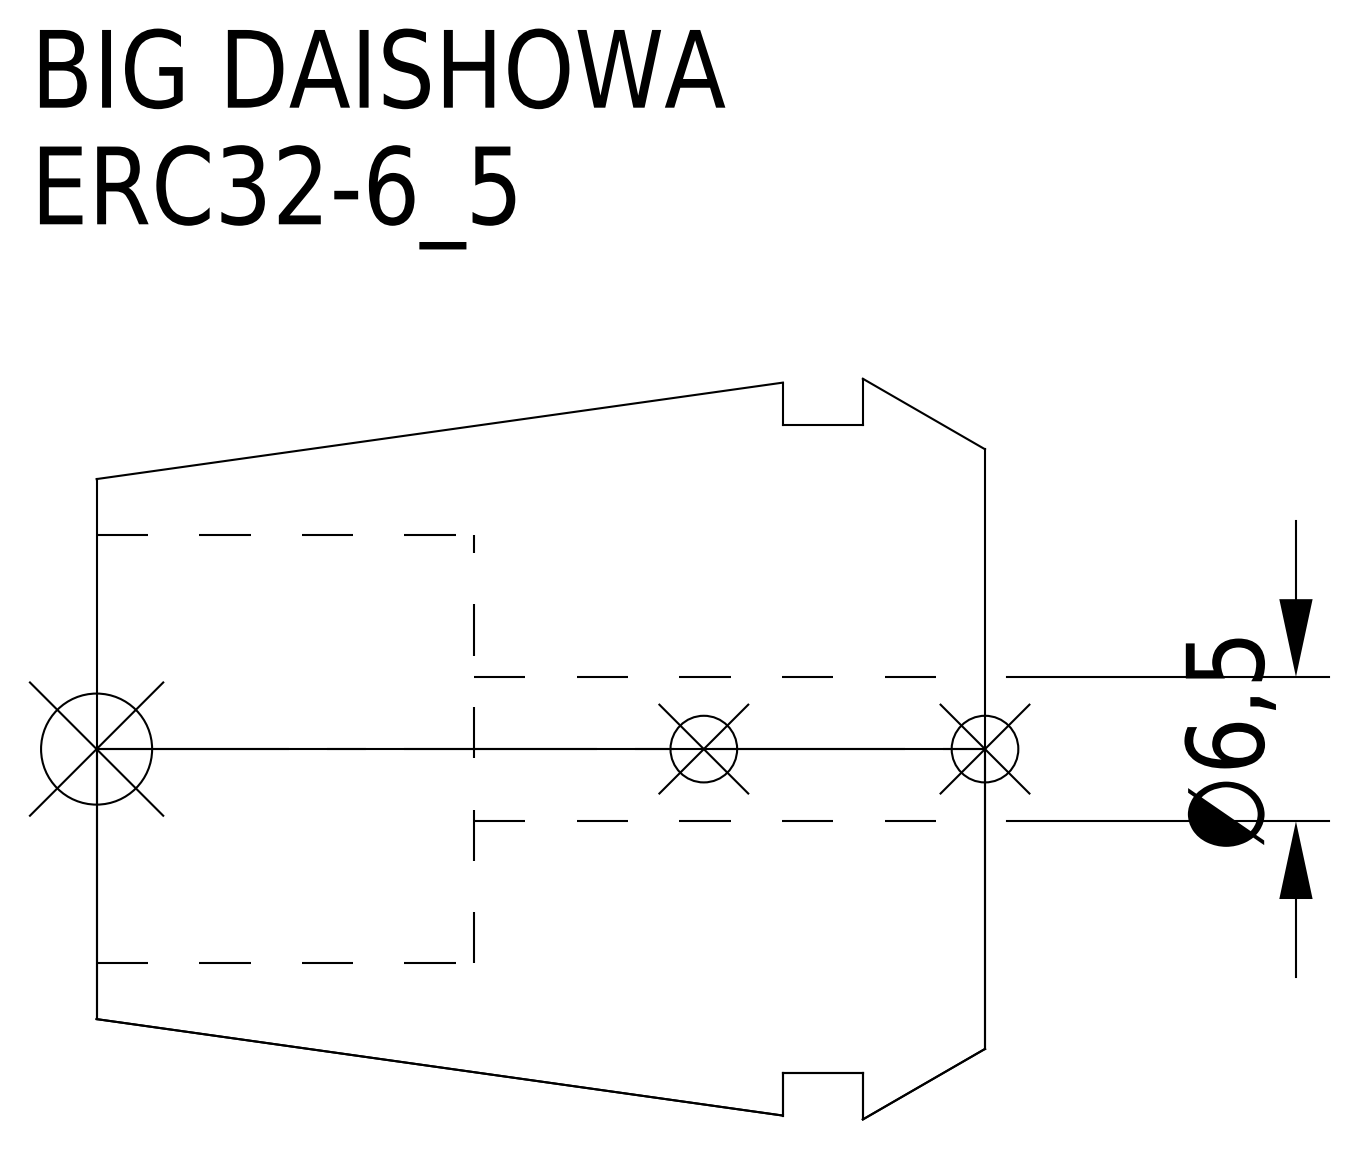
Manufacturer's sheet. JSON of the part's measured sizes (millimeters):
{"part_name": "ERC32-6_5", "step_written_by": "CREO PARAMETRIC BY PTC INC, 2016380 (AUTOMOTIVE_DESIGN)", "units": "millimeters", "bodies": {"solids": 1, "faces": 15, "planar": 5, "cylindrical": 6, "other": 4}, "overall_size": [40, 33.35, 33.35], "volume_mm3": 20706, "surface_area_mm2": 6602, "round_holes": [[6.5, 1], [19.3, 1]], "round_bosses_or_shafts": [[29.2, 1]], "face_to_face_distances": [23, 5.5, 17.5, 9.1, 3.6, 13.9, 40, 34.5, 30.9, 17]}
